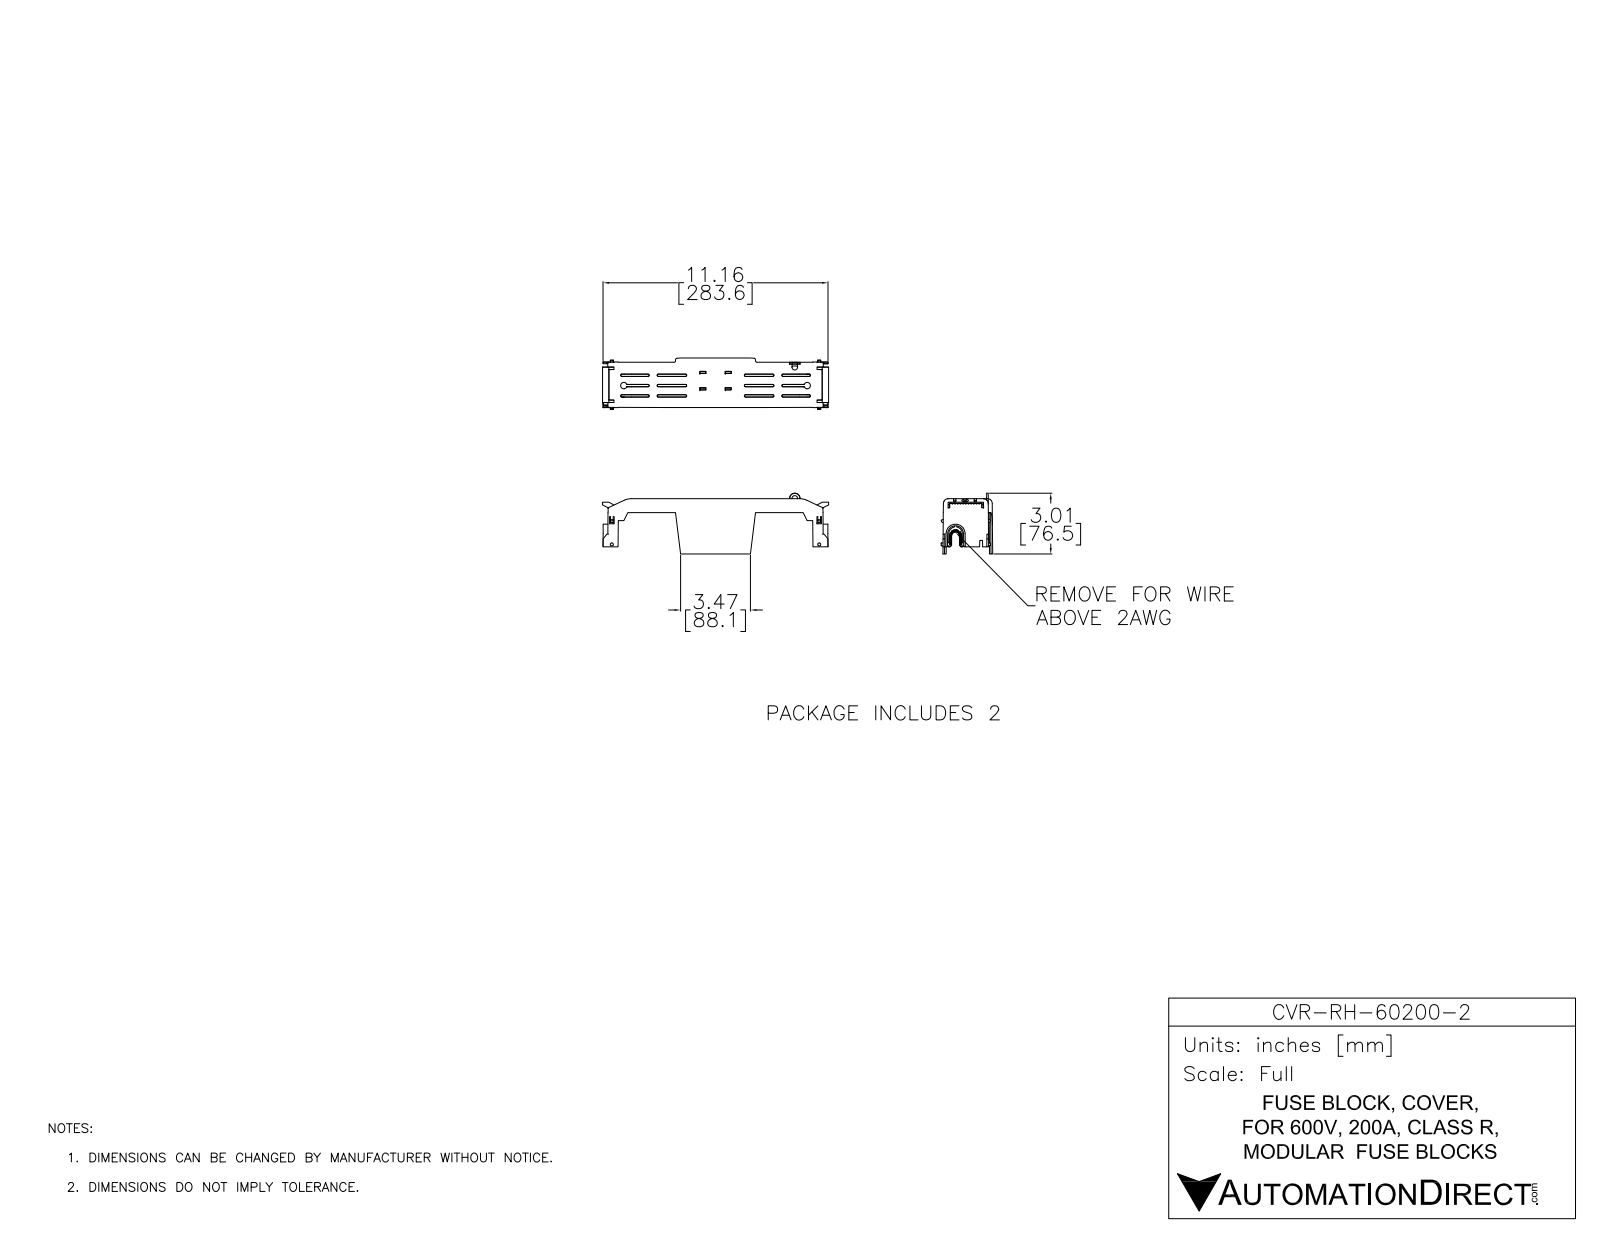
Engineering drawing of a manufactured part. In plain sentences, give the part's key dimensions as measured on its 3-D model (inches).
The part is named "CVR-RH-60200-2". Its 3-D file was written by "SolidWorks 2017 (AUTOMOTIVE_DESIGN)". It is 1 solid with 1446 faces: 937 planar, 106 cylindrical and 403 other. Overall it measures 11.215 by 3.012 by 2.553 inches. Its volume is 5.503 cubic inches and its surface area 149.2 square inches. Round holes: 1 of diameter 0.276. Partial cylindrical surfaces (rounded edges, fillets, slot ends): 16 of radius 0.039, 8 of radius 0.118, 7 of radius 0.157, 7 of radius 0.236, 6 of radius 0.079, 2 of radius 0.01, 2 of radius 0.02, 2 of radius 0.197. The main face-to-face distances are 0.079, 0.197, 0.118, 0.276, 0.512, 0.803, 0.624, 1.681, 1.76, 1.267.
